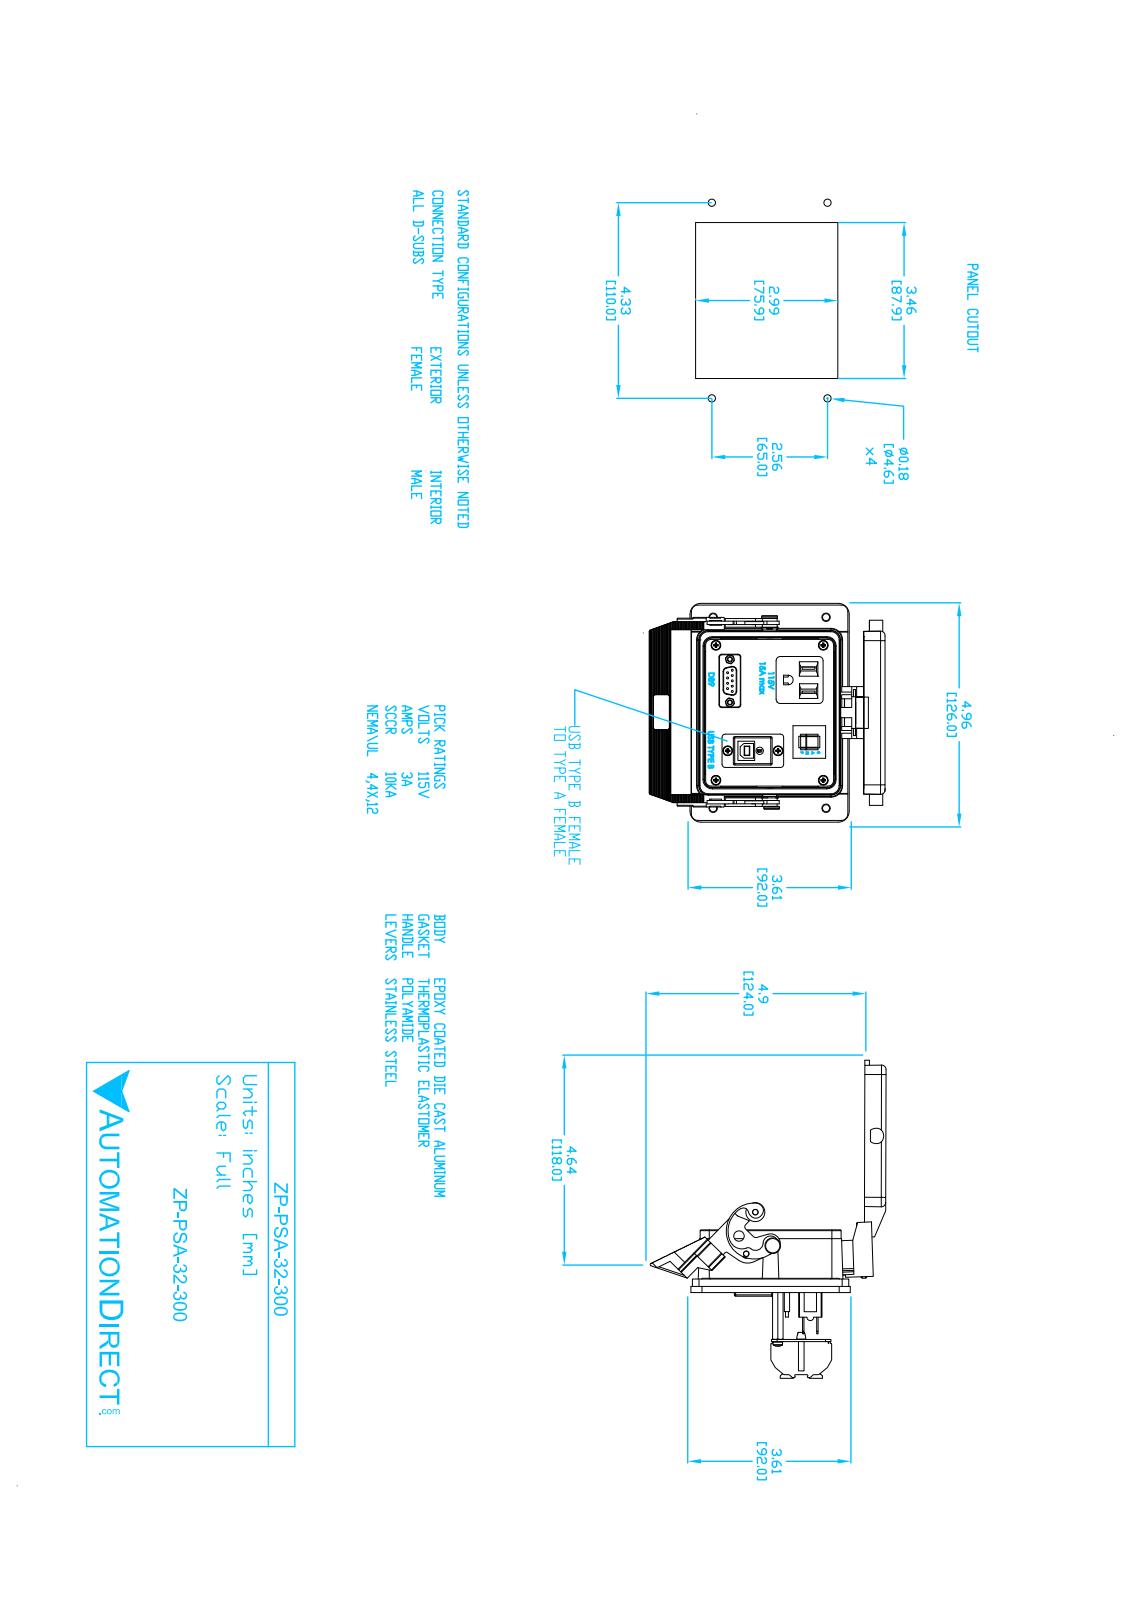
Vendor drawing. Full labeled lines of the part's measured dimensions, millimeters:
Part name (STEP PRODUCT): ZP-PSA-32-300
STEP written by: SolidWorks 2017 (AUTOMOTIVE_DESIGN)
Units: millimetres
Bodies: 1 solid, 3693 faces (2281 planar, 770 cylindrical, 642 other)
Overall size (bounding box): 195.2 × 135 × 126
Volume: 197 100 mm³ · Surface area: 120 500 mm²
Round holes (diameter × count): ⌀1.1 ×9, ⌀3.7 ×8, ⌀2.5 ×6, ⌀4.4 ×6, ⌀3.4 ×4, ⌀4.1 ×4, ⌀4.8 ×4, ⌀2.3 ×3, ⌀2.3 ×2, ⌀2.5 ×2, ⌀3 ×2, ⌀3.1 ×2
Round bosses / shafts (diameter × count): ⌀1 ×9, ⌀3 ×6, ⌀5.6 ×4, ⌀5.2 ×3, ⌀9 ×2, ⌀2.8 ×2, ⌀2.4 ×2, ⌀10.9 ×1
Partial cylindrical surfaces — rounded edges, fillets, slot ends (radius × count): R0.3 ×24, R0.5 ×22, R2.5 ×18, R0.5 ×17, R0.6 ×12, R6.4 ×12, R0.2 ×10, R0.4 ×9
Main face-to-face distances: 3.4, 21.5, 23, 1.5, 61.1, 39.6, 62.6, 16.8, 45.9, 6.3
Hole centre spacings: 3, 12, 6, 26.9, 32.7, 34.9, 39.9, 61.9
